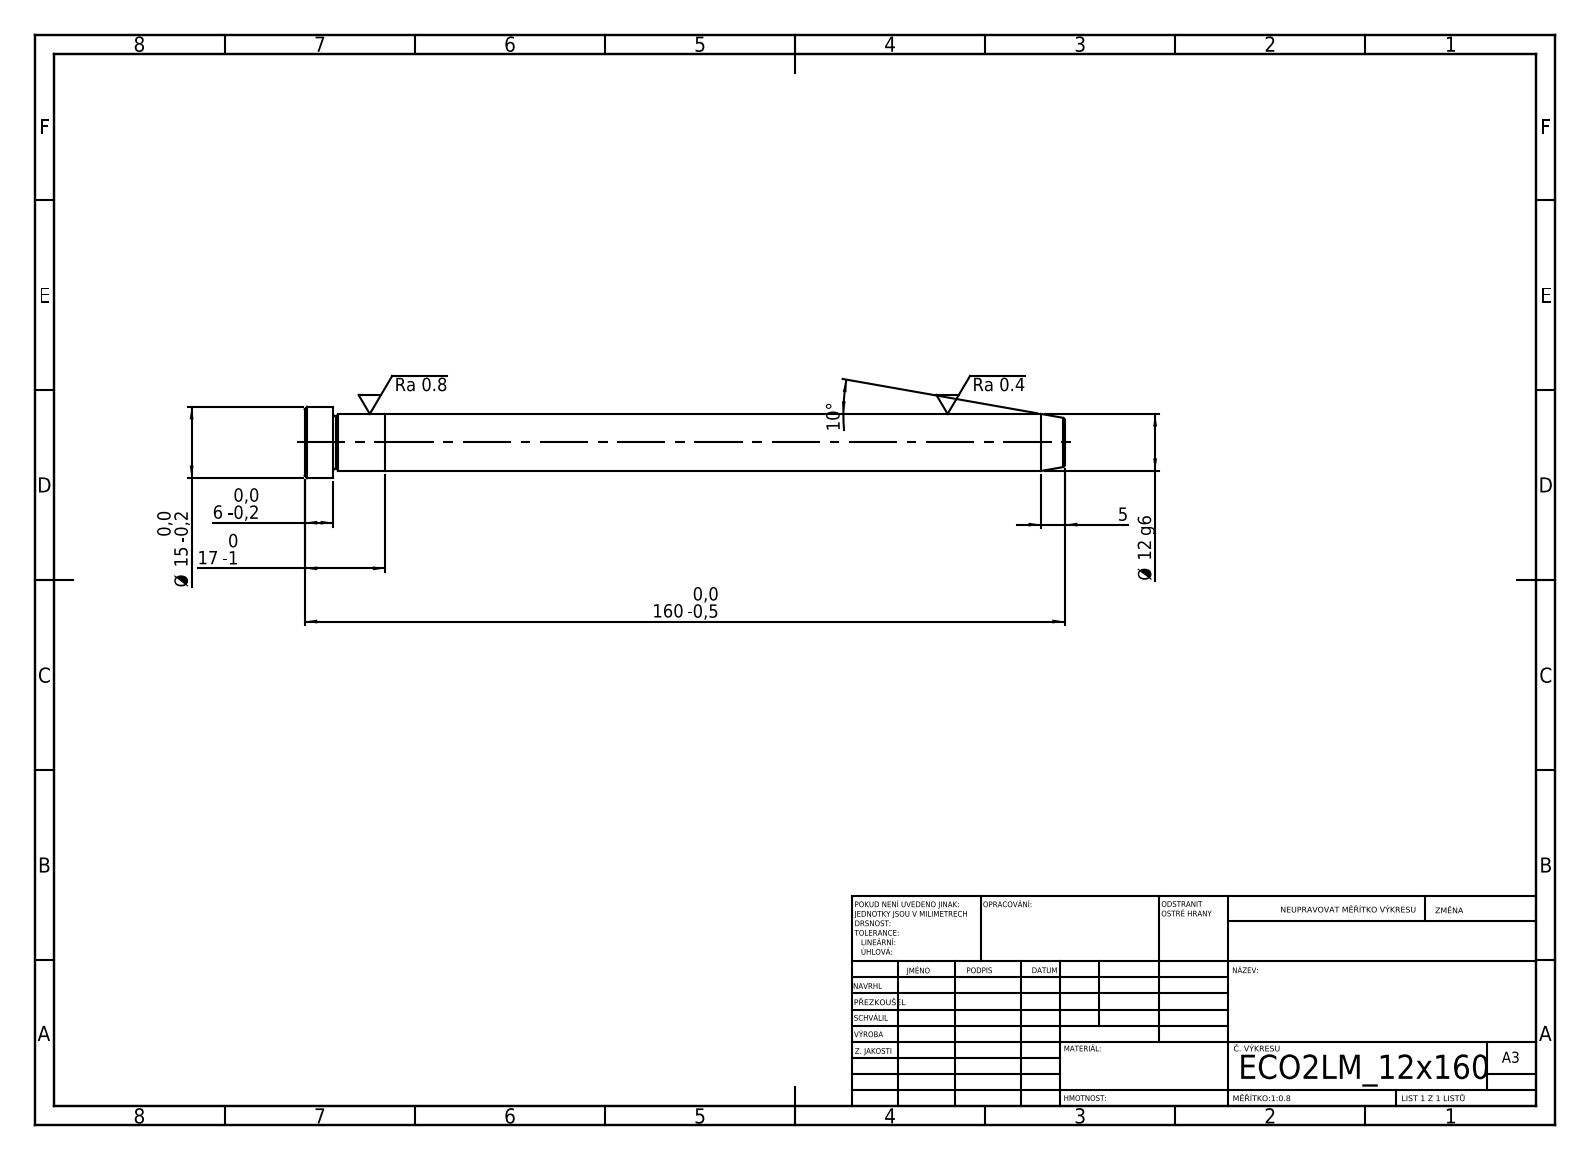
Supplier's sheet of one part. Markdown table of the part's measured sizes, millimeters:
| quantity | value |
| --- | --- |
| STEP written by | SolidWorks 2019 (CONFIG_CONTROL_DESIGN) |
| units | millimeters |
| bodies | 2 solids, 21 faces (5 planar, 6 cylindrical, 10 other) |
| overall size | 160 × 15 × 15 |
| volume | 18 377 mm³ |
| surface area | 6 626 mm² |
| round bosses / shafts (diameter × count) | 15 × 1, 12 × 1 |
| main face-to-face distances | 17, 143, 160, 154, 11, 6 |
